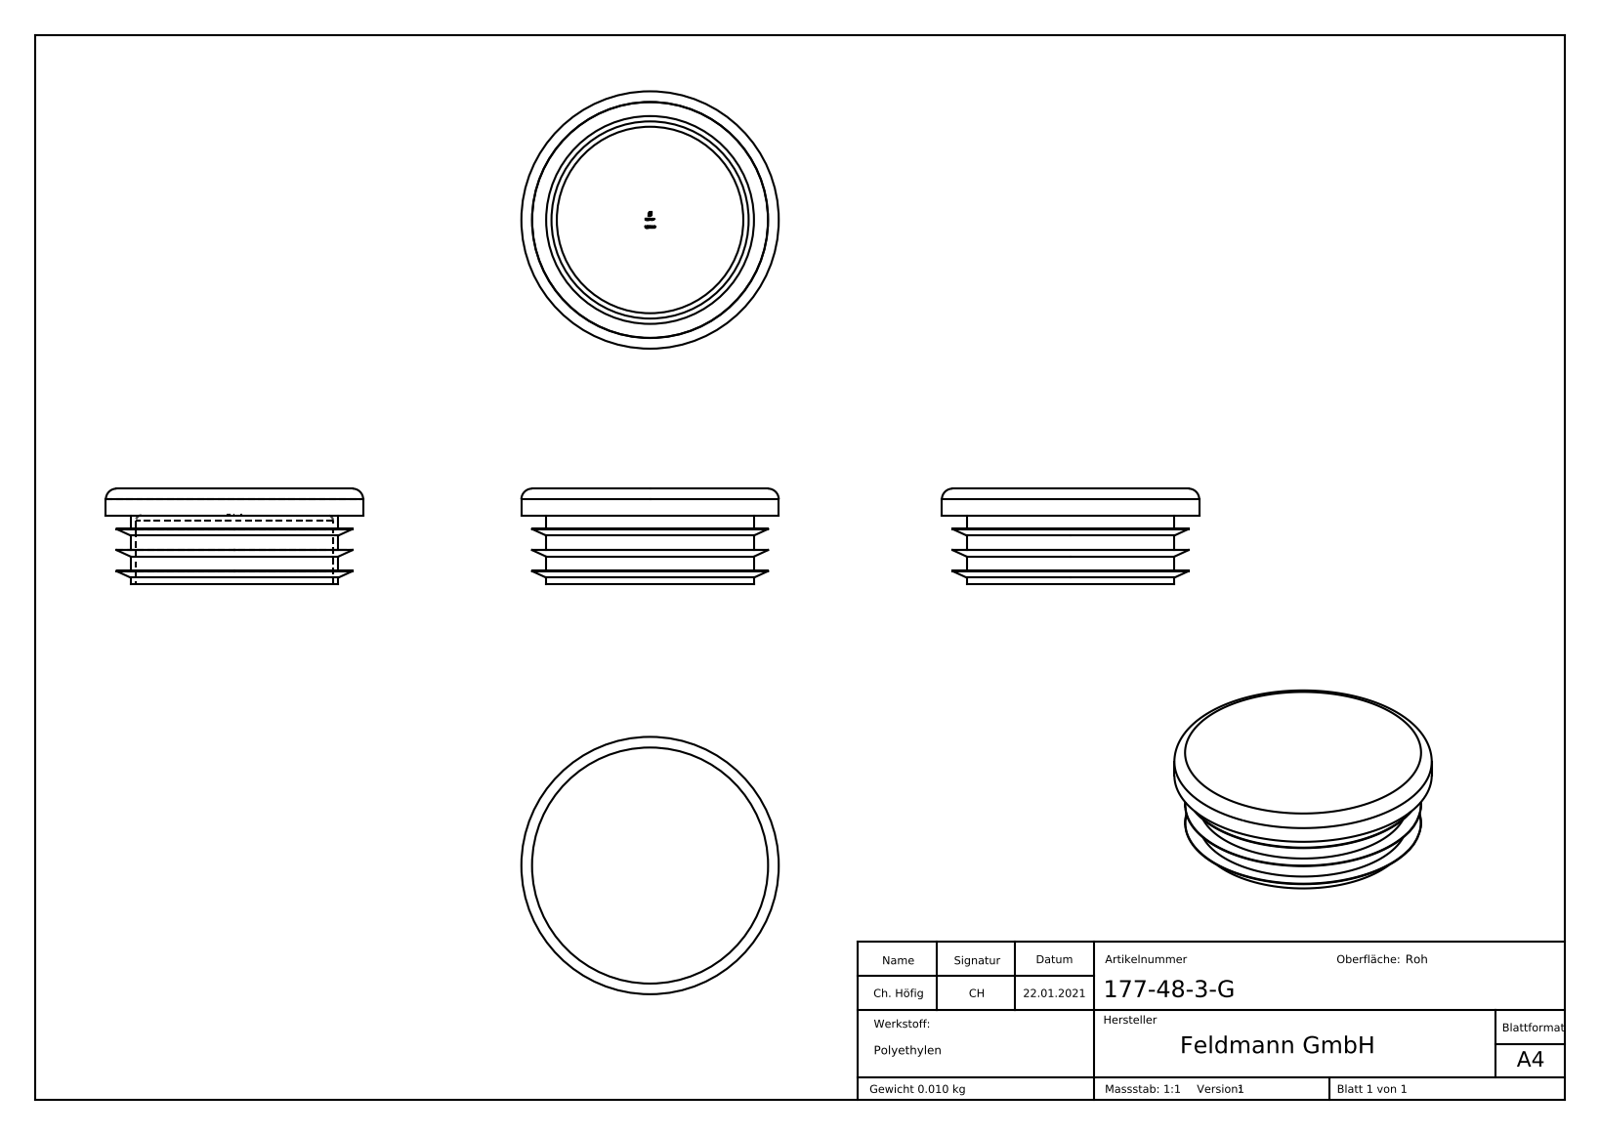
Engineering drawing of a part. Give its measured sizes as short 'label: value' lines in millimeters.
name: 177-48-3-G
written by: SolidWorks 2018 (CONFIG_CONTROL_DESIGN)
unit: mm
bodies: 1 solid, 292 faces (156 planar, 12 cylindrical, 124 other)
size: 48.3 × 48.3 × 18
volume: 11 315 mm³; area: 9 077 mm²
holes: 1× ⌀37
bosses: 1× ⌀48.3, 1× ⌀39
face distances: 5, 3.95, 7.9, 10.4, 15.4, 6.45, 11.45, 2.5, 7.5, 2.6
